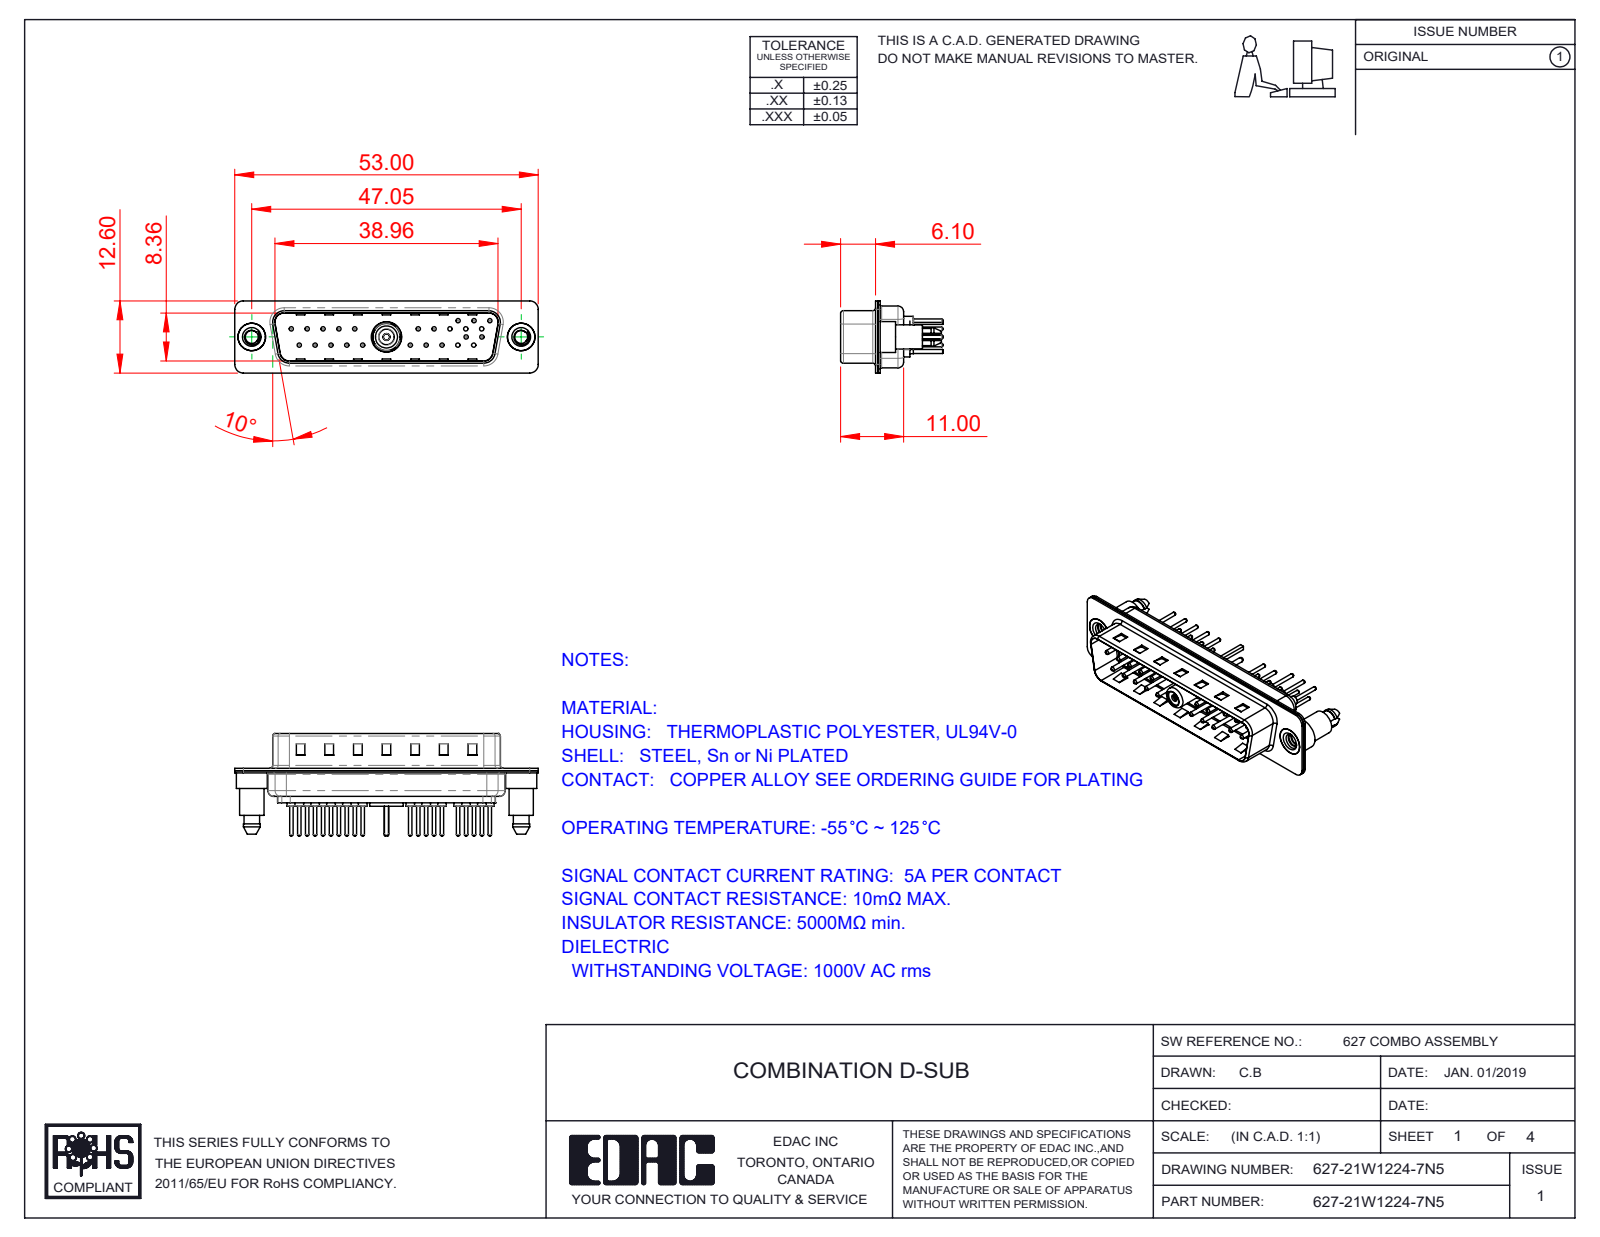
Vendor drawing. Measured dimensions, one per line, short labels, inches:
name: 627Combo Contact Row 1_24; Co-Ax Jack Assy_S; Locking Collar; 627Combo Threaded Boardlock_5 (+8 more)
written by: SolidWorks 2016 (CONFIG_CONTROL_DESIGN)
unit: in
bodies: 30 solids, 1277 faces (374 planar, 496 cylindrical, 407 other)
size: 2.087 × 0.705 × 0.496
volume: 0.175 in³; area: 11.73 in²
holes: 21× ⌀0.063, 20× ⌀0.03, 20× ⌀0.079, 2× ⌀0.089, 2× ⌀0.157, 2× ⌀0.189, 1× ⌀0.043, 1× ⌀0.047, 1× ⌀0.059, 1× ⌀0.098, 1× ⌀0.106, 1× ⌀0.134
bosses: 20× ⌀0.059, 20× ⌀0.024, 5× ⌀0.079, 5× ⌀0.03, 2× ⌀0.213, 2× ⌀0.193, 2× ⌀0.167, 1× ⌀0.23
rounds: 18× R0.059, 12× R0.079, 10× R0.063, 8× R0.02, 4× R0.01, 4× R0.024, 4× R0.026, 4× R0.035
face distances: 0.016, 0.032, 0.377, 0.345, 0.059, 0.205, 0.236, 0.031, 0.22, 0.048
hole spacings: 0.124, 0.109, 0.218, 0.327, 0.198, 0.763, 0.826, 0.872
